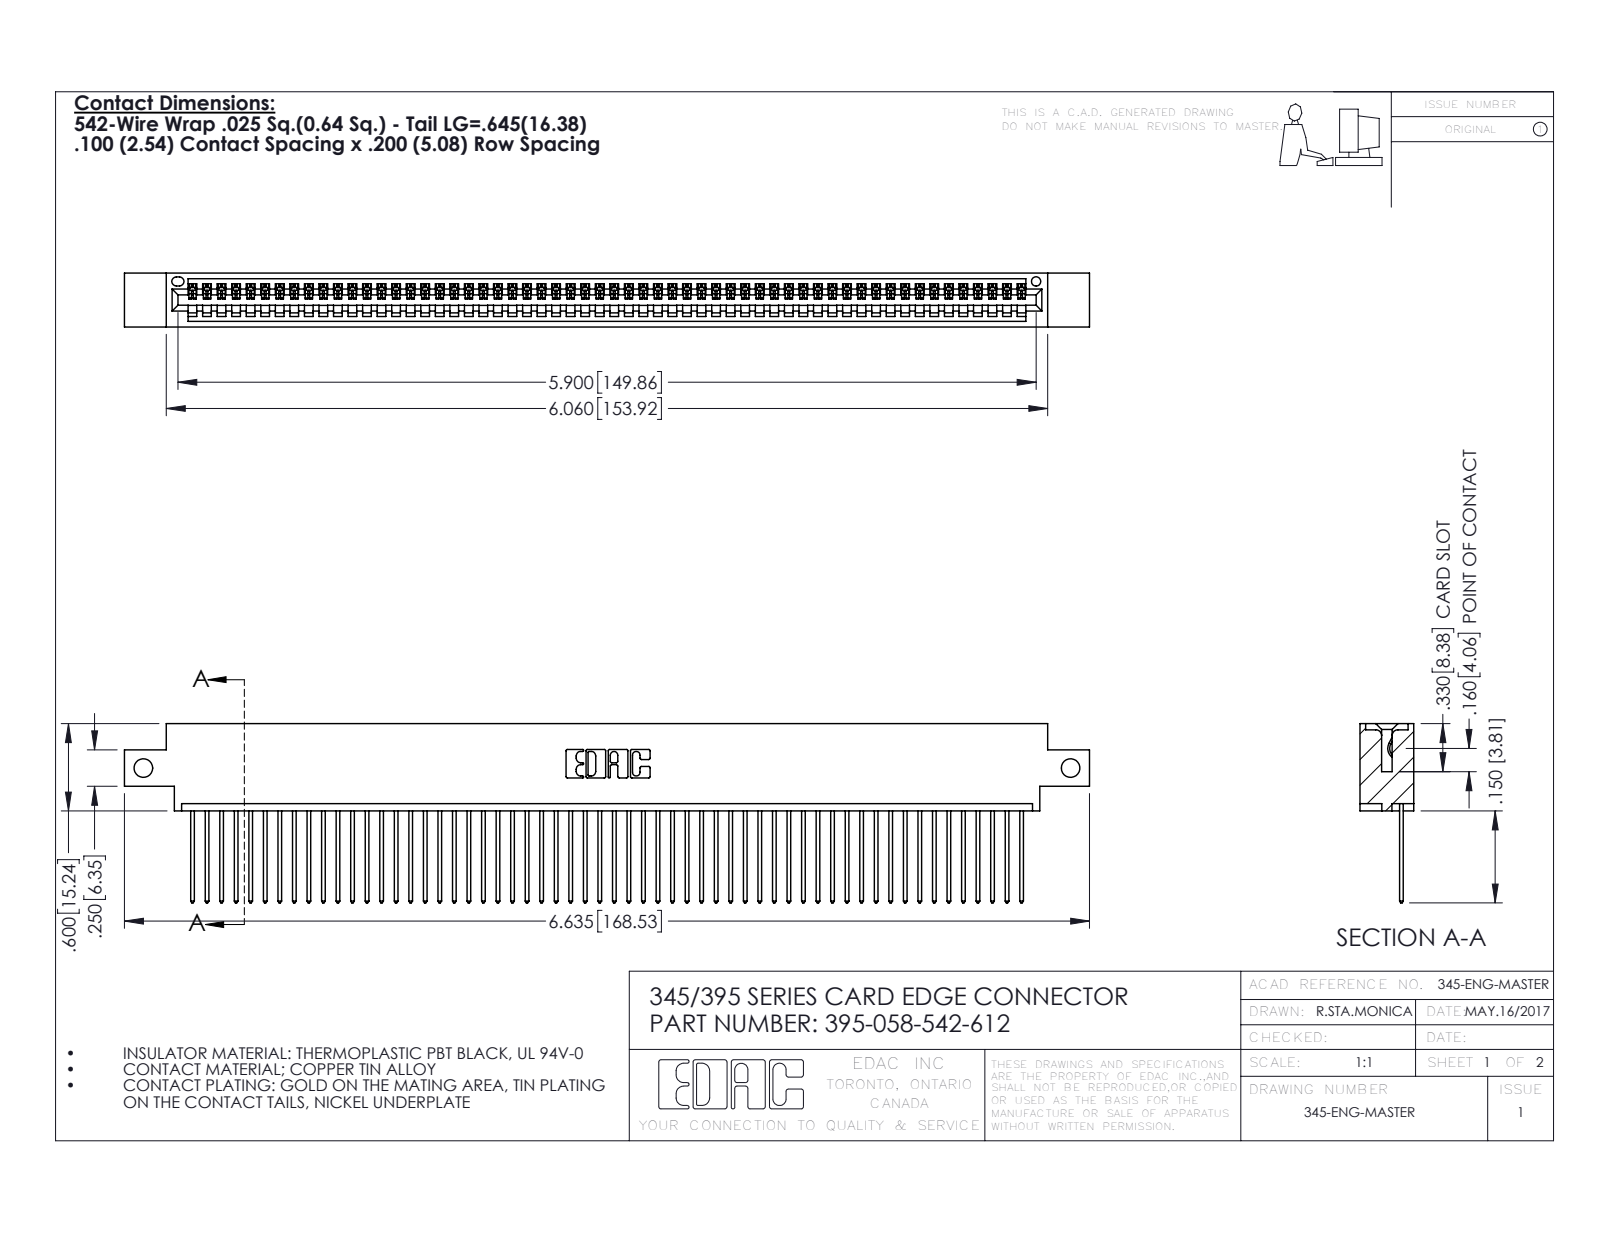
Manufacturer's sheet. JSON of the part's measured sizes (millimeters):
{"part_name": "345-292-001_345-293-142; 395-058-542-612; 345 Part_0.170 Offset - Side Mount", "step_written_by": "SolidWorks 2016 (CONFIG_CONTROL_DESIGN)", "units": "millimeters", "bodies": {"solids": 59, "faces": 3494, "planar": 2404, "cylindrical": 1090, "other": 0}, "overall_size": [168.5, 31.3, 9.4], "volume_mm3": 16100, "surface_area_mm2": 22370, "round_holes": [[3.3, 2], [1.6, 1]], "partial_cylinders_radius": [[0.2, 116], [0.3, 116], [0.3, 22], [0.2, 6], [0.8, 6], [0.7, 3], [0.8, 2], [1, 2]], "face_to_face_distances": [1.8, 7.6, 9.4, 2.5, 6.9, 0.6, 5.1, 5.7, 4.4, 3.8], "hole_center_spacings": [161.9]}
